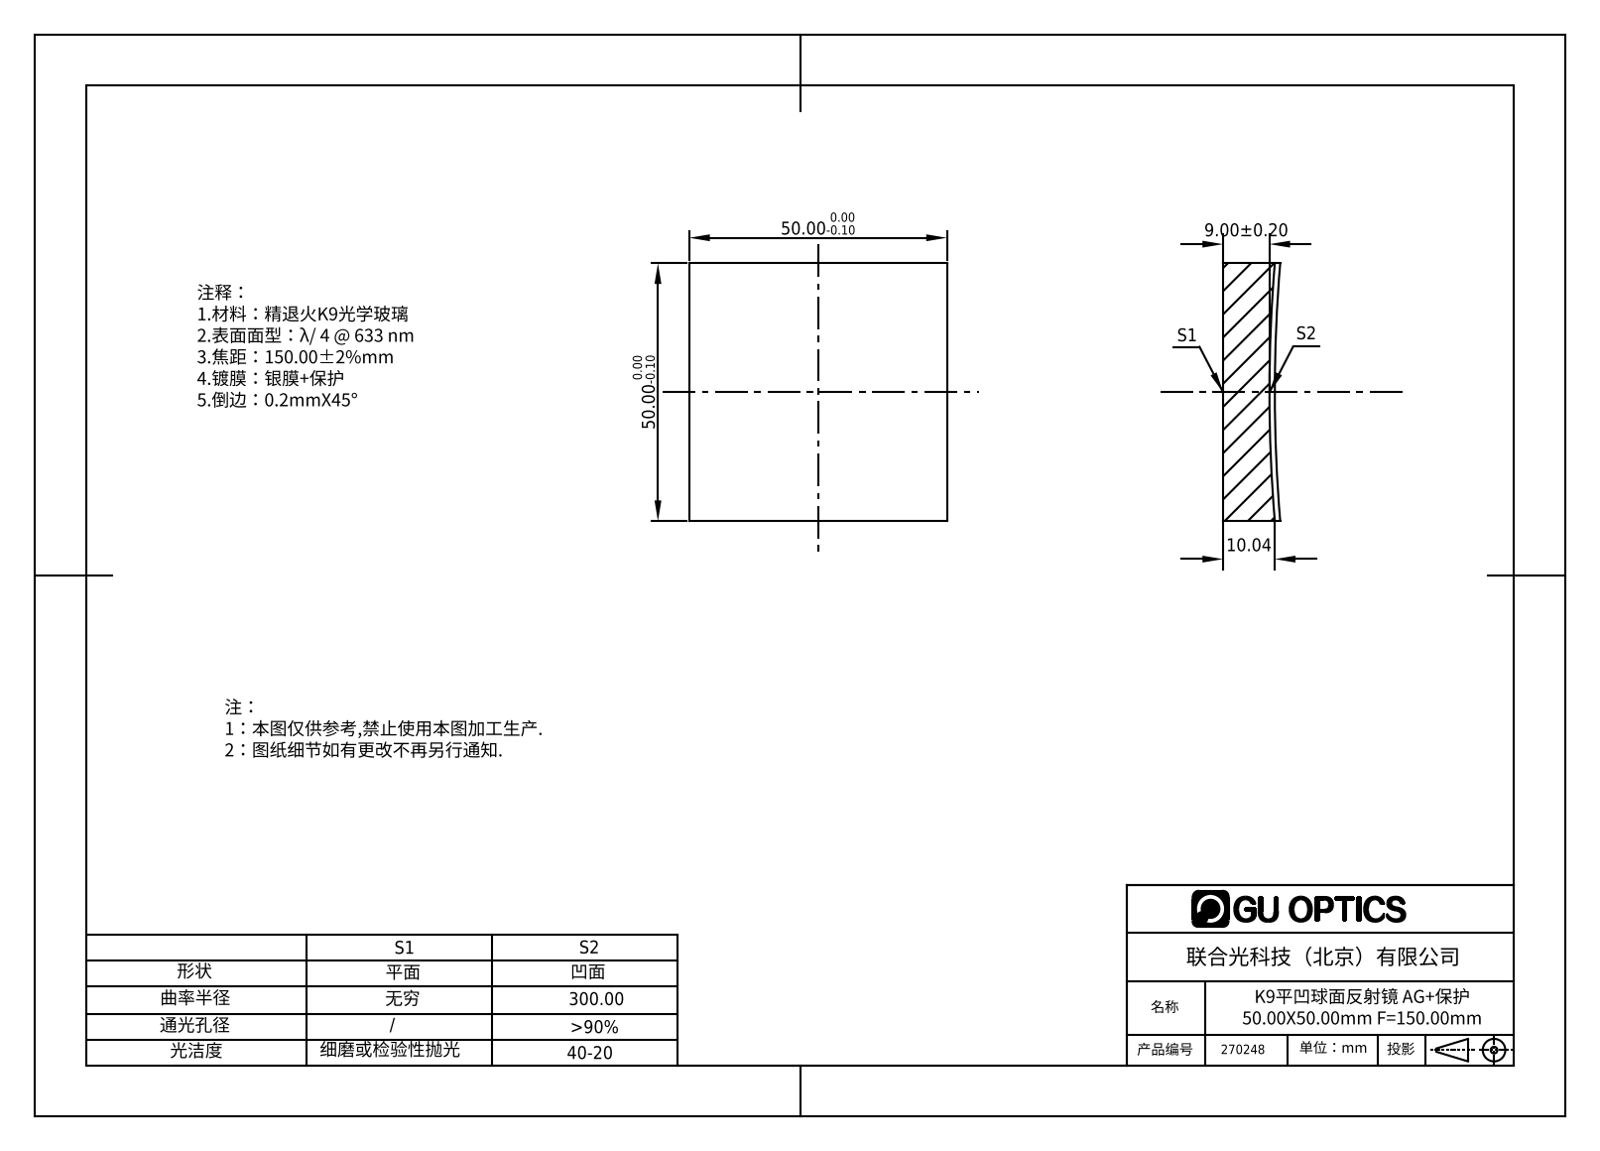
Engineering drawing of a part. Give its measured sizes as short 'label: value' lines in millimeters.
name: 270053
written by: SolidWorks 2019 (AUTOMOTIVE_DESIGN)
unit: mm
bodies: 1 solid, 7 faces (5 planar, 0 cylindrical, 2 other)
size: 50 × 50 × 11.09
volume: 24 239 mm³; area: 7 084 mm²
face distances: 50
